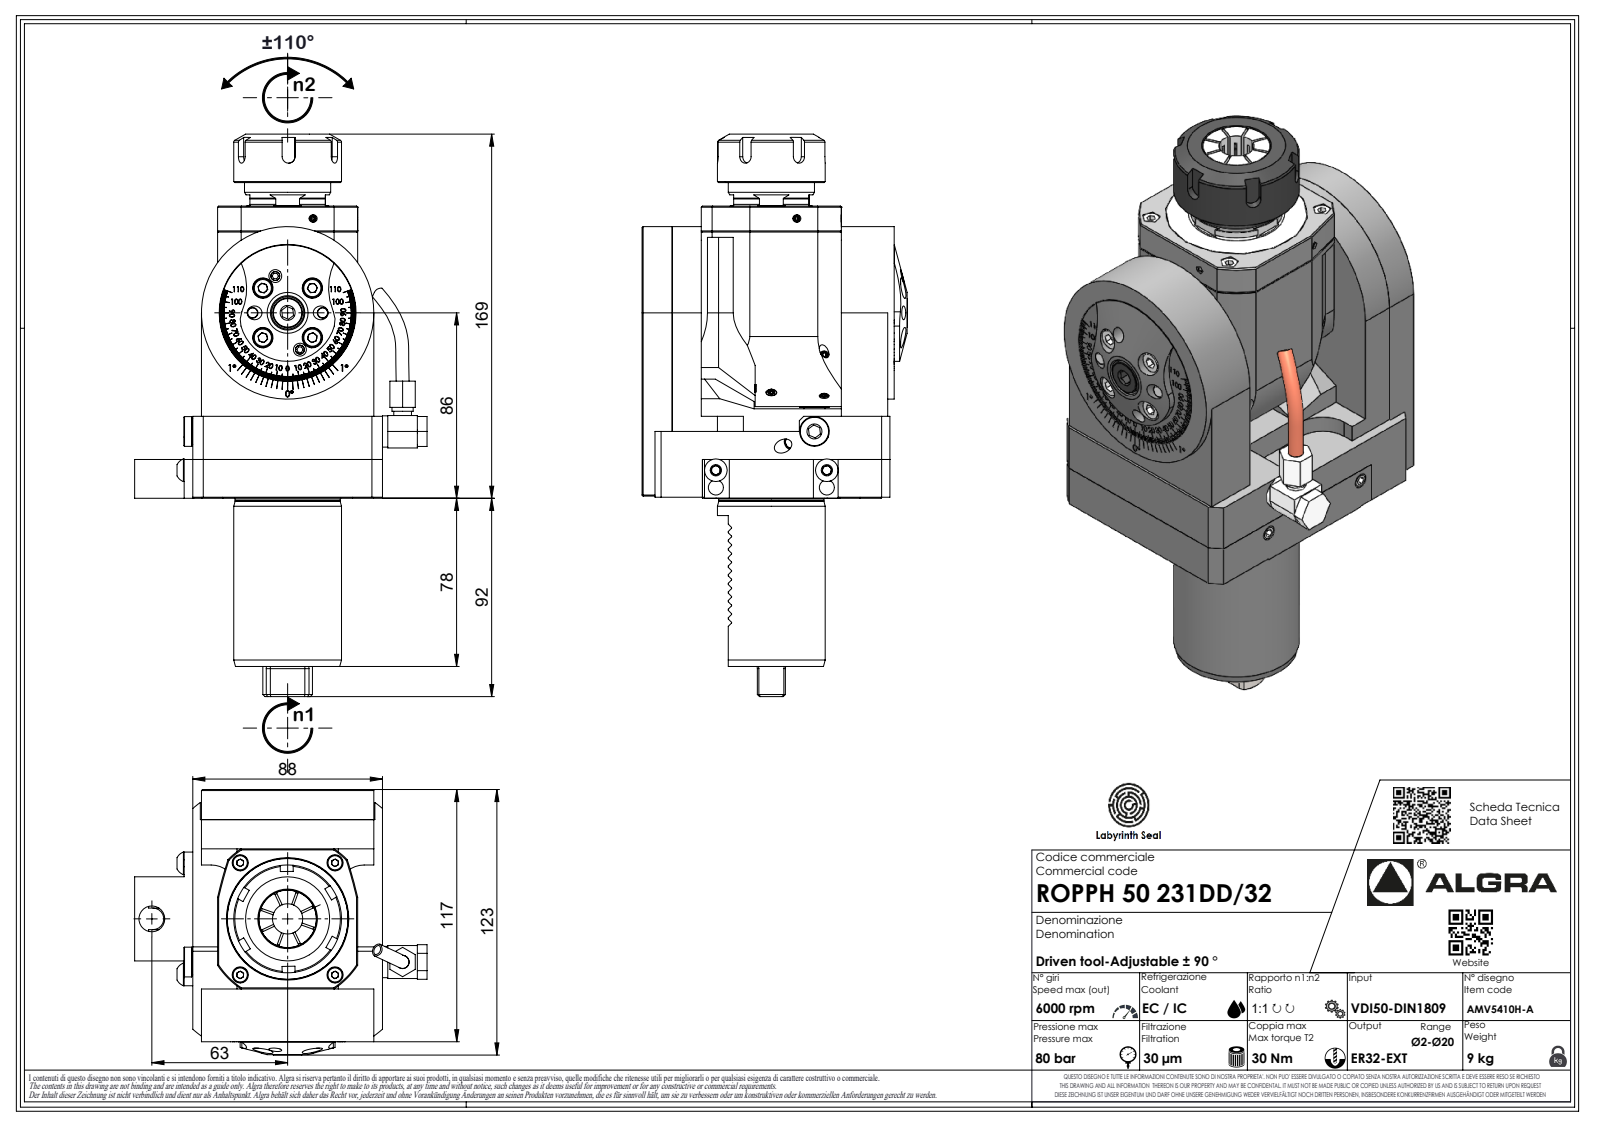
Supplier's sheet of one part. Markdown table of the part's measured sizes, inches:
| quantity | value |
| --- | --- |
| part name | ROPPH50231DD32 |
| STEP written by | SolidWorks 2023 (AUTOMOTIVE_DESIGN) |
| units | inches |
| bodies | 1 solid, 645 faces (408 planar, 98 cylindrical, 139 other) |
| overall size | 10.272 × 5.343 × 4.843 |
| volume | 77.62 in³ |
| surface area | 171.4 in² |
| round holes (diameter × count) | 0.083 × 1 |
| round bosses / shafts (diameter × count) | 3.15 × 1, 1.969 × 1, 1.917 × 1, 1.575 × 1, 0.571 × 1, 0.386 × 1, 0.323 × 1, 0.251 × 1 |
| partial cylindrical surfaces (radius × count) | 0.012 × 12, 0.118 × 11, 0.013 × 7, 0.02 × 7, 0.146 × 7, 0.394 × 2, 0.472 × 2, 1.102 × 2 |
| main face-to-face distances | 0.157, 3.307, 2.559, 0.02, 3.012, 0.453, 0.295, 0.965, 2.854, 1.083 |
